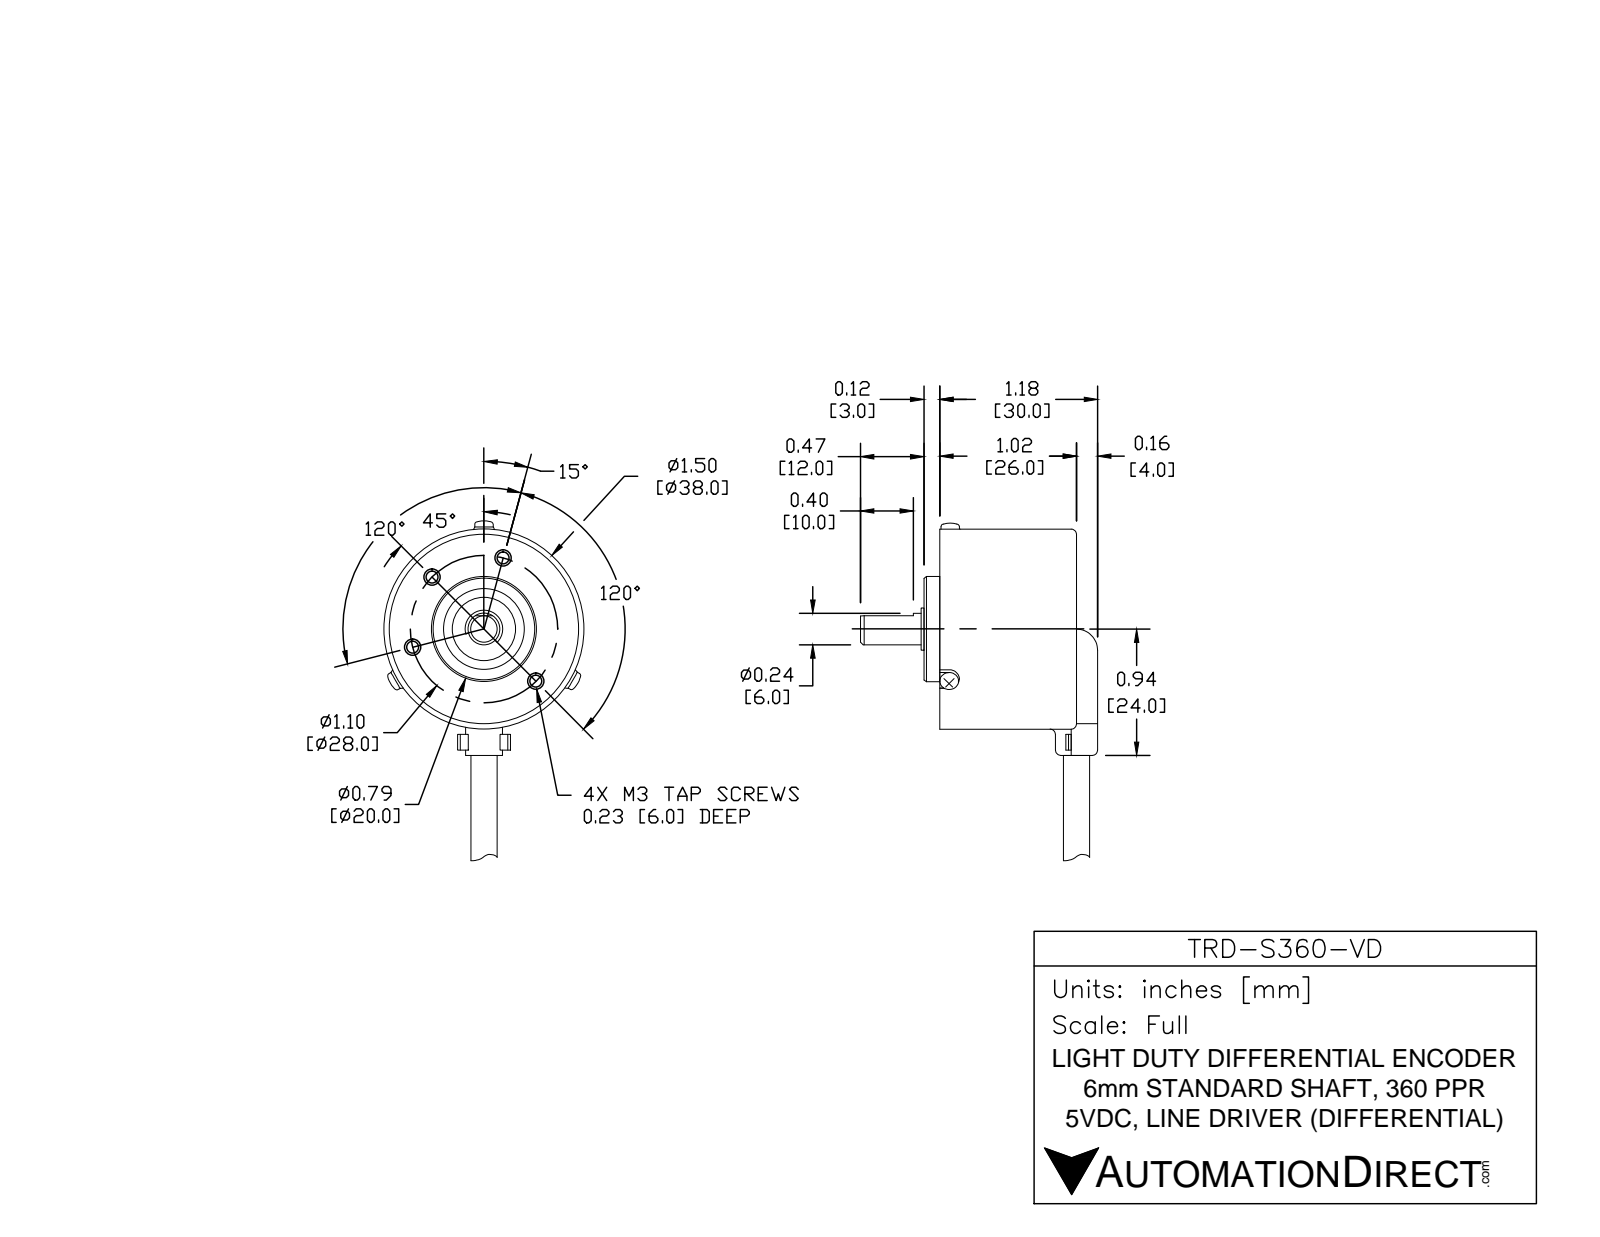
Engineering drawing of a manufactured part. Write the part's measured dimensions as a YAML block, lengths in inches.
part_name: "TRD-S"
step_written_by: "SolidWorks 2016 (AUTOMOTIVE_DESIGN)"
units: inches
bodies: {solids: 1, faces: 178, planar: 61, cylindrical: 72, other: 45}
overall_size: [7.189, 1.768, 1.496]
volume: 2.057
surface_area: 13.74
round_holes:
  - {diameter: 0.118, count: 4}
  - {diameter: 0.205, count: 1}
  - {diameter: 1.409, count: 1}
round_bosses_or_shafts:
  - {diameter: 1.496, count: 1}
  - {diameter: 0.787, count: 1}
  - {diameter: 0.591, count: 1}
  - {diameter: 0.315, count: 1}
  - {diameter: 0.236, count: 1}
  - {diameter: 0.197, count: 1}
  - {diameter: 0.193, count: 1}
partial_cylinders:
  - {radius: 0.02, count: 5}
  - {radius: 0.004, count: 4}
  - {radius: 0.039, count: 4}
  - {radius: 0.079, count: 3}
  - {radius: 0.13, count: 3}
  - {radius: 0.008, count: 2}
  - {radius: 0.031, count: 2}
  - {radius: 0.102, count: 1}
face_to_face_distances: [1.024, 0.118, 1.142, 0.043, 0.98, 1.098, 0.335, 0.217, 0.138, 0.354]
hole_center_spacings: [0.551, 0.955, 0.954, 1.102]
